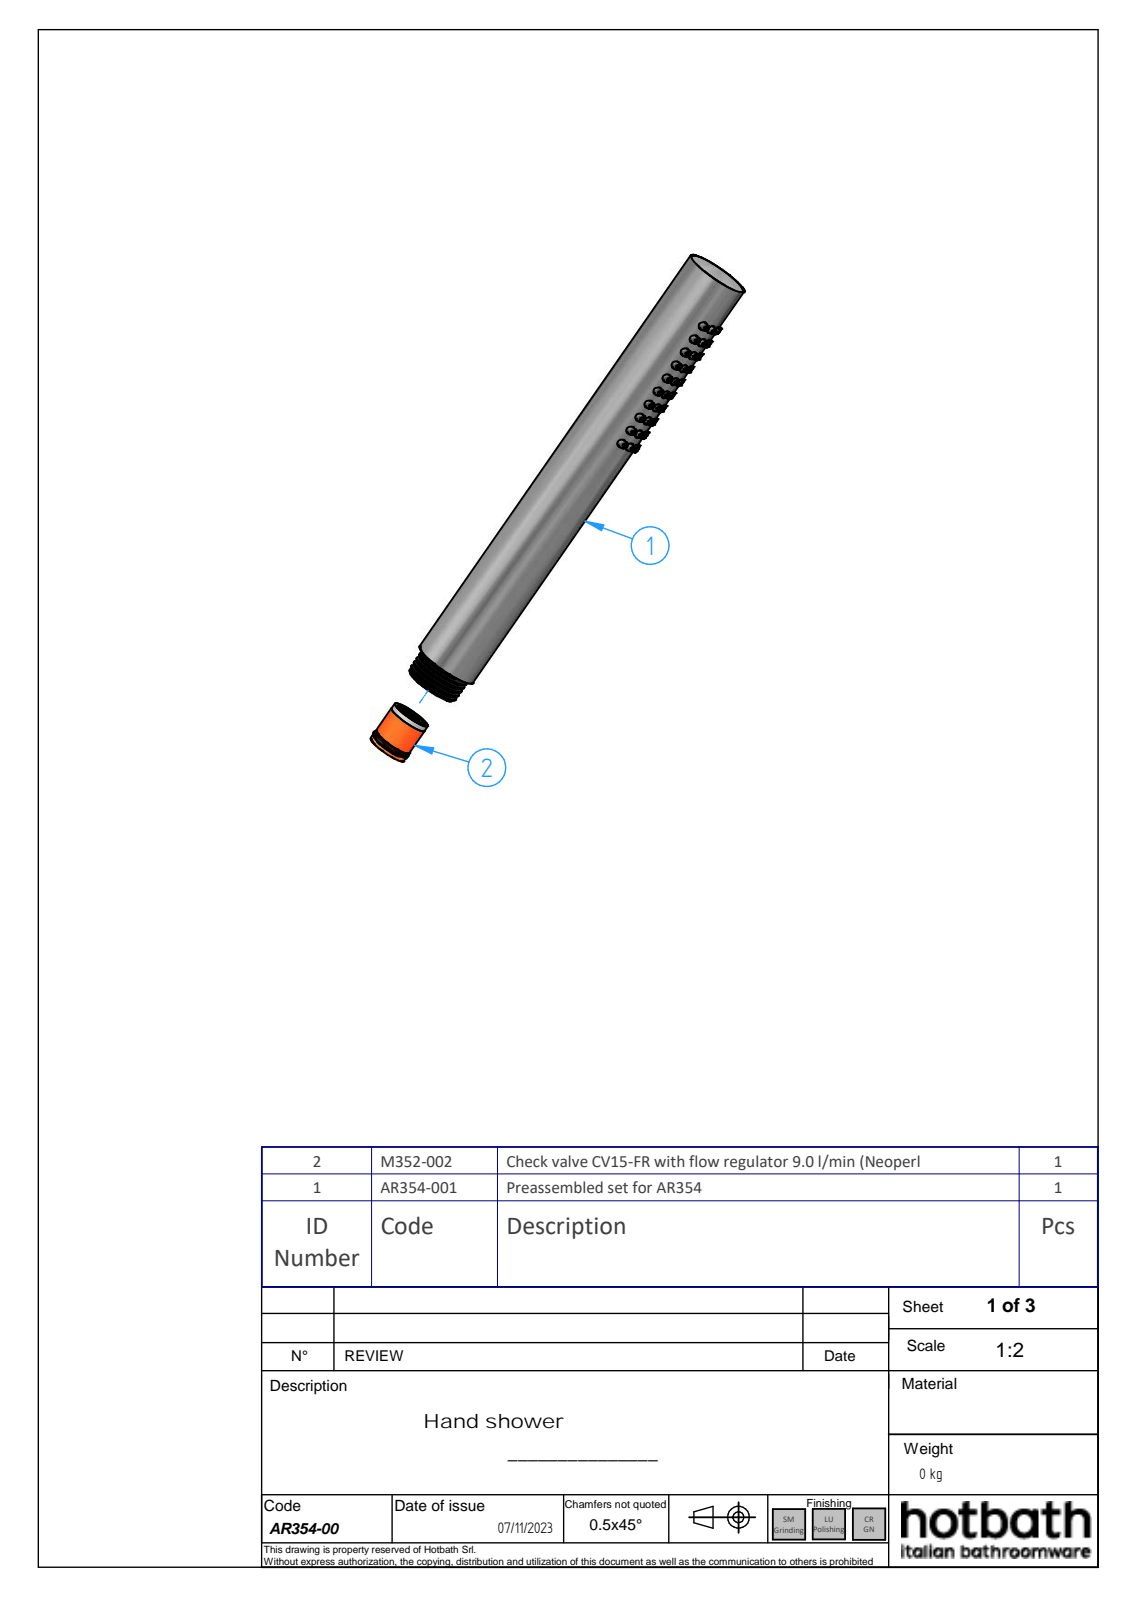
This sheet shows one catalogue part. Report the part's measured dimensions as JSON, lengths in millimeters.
{"part_name": "AR354-00; AR354-001_oa_0; AR354-01; A133037_13400ZZ_oa_1 (+2 more)", "step_written_by": "Solid Edge (AUTOMOTIVE_DESIGN)", "units": "millimeters", "bodies": {"solids": 4, "faces": 553, "planar": 66, "cylindrical": 140, "other": 347}, "overall_size": [190.36, 25.15, 24], "volume_mm3": 19560, "surface_area_mm2": 36174, "round_holes": [[3.2, 40], [3.24, 1], [22, 1], [23, 1]], "round_bosses_or_shafts": [[24, 1], [21.8, 1], [20.8, 1], [18.8, 1], [18.6, 1]], "partial_cylinders_radius": [[0.35, 4], [0.59, 3], [0.2, 2], [0.22, 2], [0.23, 2], [0.28, 2], [0.4, 2], [0.5, 2]], "face_to_face_distances": [1.4, 1.65, 1.5, 10, 170.49, 2, 171.99, 173.99, 3.5, 16.9], "hole_center_spacings": [7.21, 12.65, 12, 6, 18.44, 4, 24.33, 10]}
